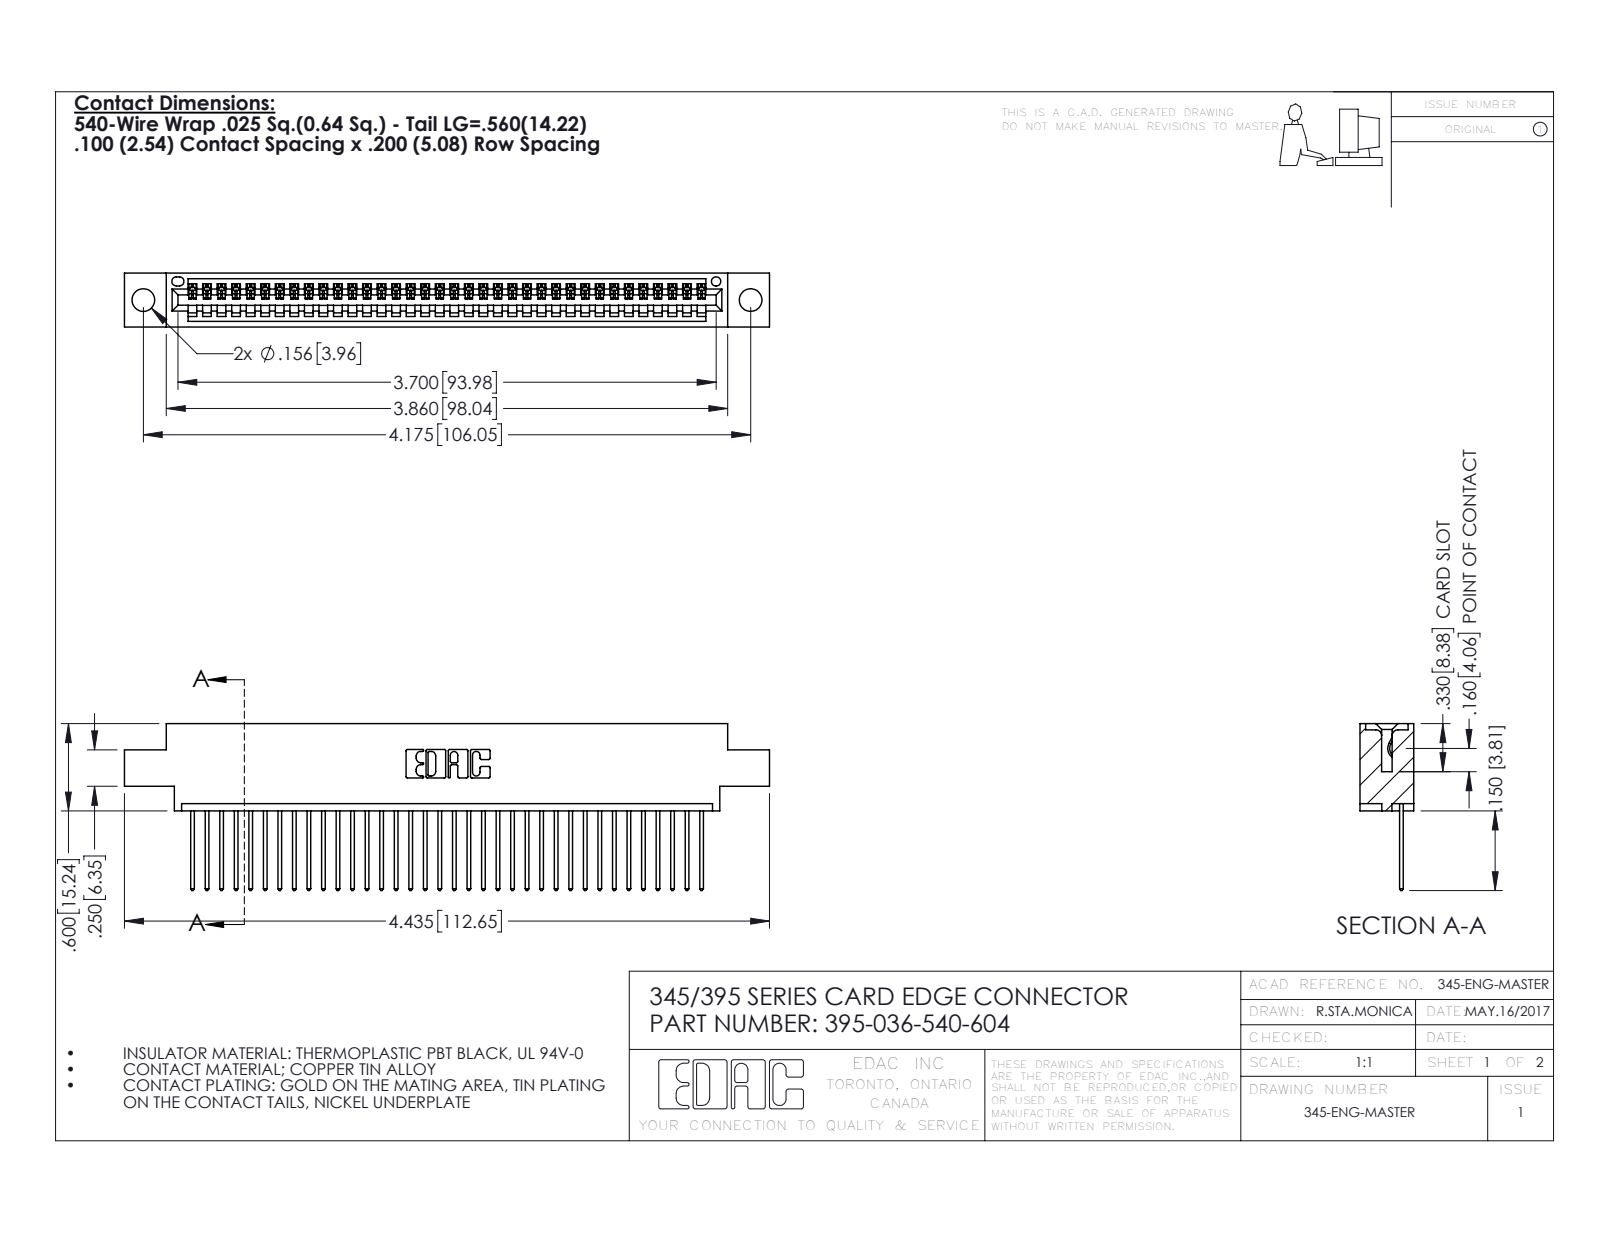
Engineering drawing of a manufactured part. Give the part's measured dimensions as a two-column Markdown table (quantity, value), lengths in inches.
| quantity | value |
| --- | --- |
| part name | 395-036-540-604; 345 Part_0.170 Offset - 0.156 Dia-TH; 345-292-001_345-293-140 |
| STEP written by | SolidWorks 2016 (CONFIG_CONTROL_DESIGN) |
| units | inches |
| bodies | 37 solids, 2218 faces (1524 planar, 694 cylindrical, 0 other) |
| overall size | 4.435 × 1.147 × 0.37 |
| volume | 0.641 in³ |
| surface area | 21.94 in² |
| round holes (diameter × count) | 0.156 × 2, 0.064 × 1 |
| partial cylindrical surfaces (radius × count) | 0.006 × 72, 0.01 × 72, 0.01 × 22, 0.007 × 6, 0.031 × 6, 0.026 × 3, 0.031 × 2, 0.04 × 2 |
| main face-to-face distances | 0.298, 0.072, 0.37, 0.098, 0.272, 0.025, 0.2, 0.225, 0.175, 0.149 |
| hole center spacings | 0.27, 3.939, 4.175 |
